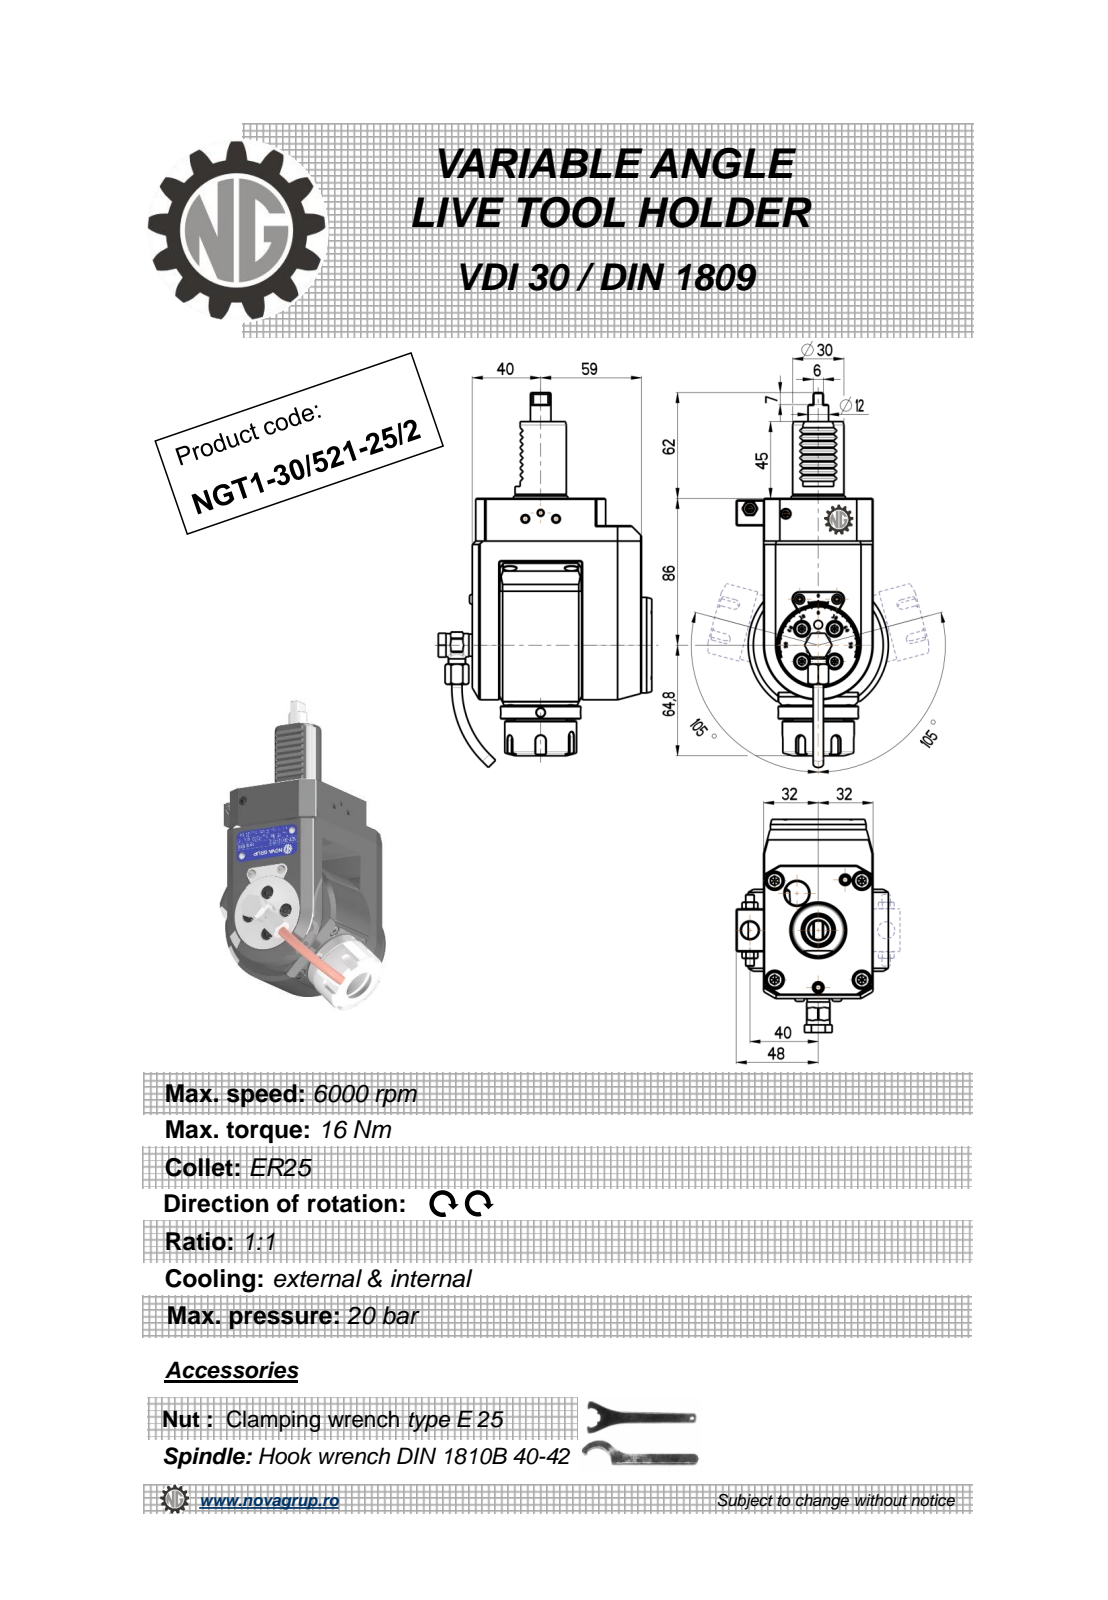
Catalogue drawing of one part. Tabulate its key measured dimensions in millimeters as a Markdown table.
| quantity | value |
| --- | --- |
| part name | NGT1_30_521_25_2 |
| STEP written by | PRO/ENGINEER BY PARAMETRIC TECHNOLOGY CORPORATION, 2010280 (CONFIG_CONTROL_DESIGN) |
| units | millimeters |
| bodies | 1 solid, 548 faces (235 planar, 138 cylindrical, 175 other) |
| overall size | 219.67 × 124.9 × 89 |
| volume | 791 329 mm³ |
| surface area | 73 509 mm² |
| round holes (diameter × count) | 4 × 5, 10 × 2, 3 × 1, 4.2 × 1, 6.2 × 1, 9 × 1, 9.5 × 1, 11 × 1, 20.3 × 1 |
| round bosses / shafts (diameter × count) | 6 × 2, 5.7 × 2, 56 × 1, 42 × 1, 40 × 1, 32.99 × 1, 30 × 1, 13.6 × 1 |
| partial cylindrical surfaces (radius × count) | 0.26 × 12, 0.3 × 8, 0.16 × 6, 0.5 × 6, 3 × 5, 1 × 2, 7.7 × 1, 32 × 1 |
| main face-to-face distances | 64, 16, 37, 6, 99, 105, 21, 14, 62, 35 |
| hole center spacings | 0.4, 38.95, 40, 49, 49.4, 63.25, 63.56, 89.44 |
